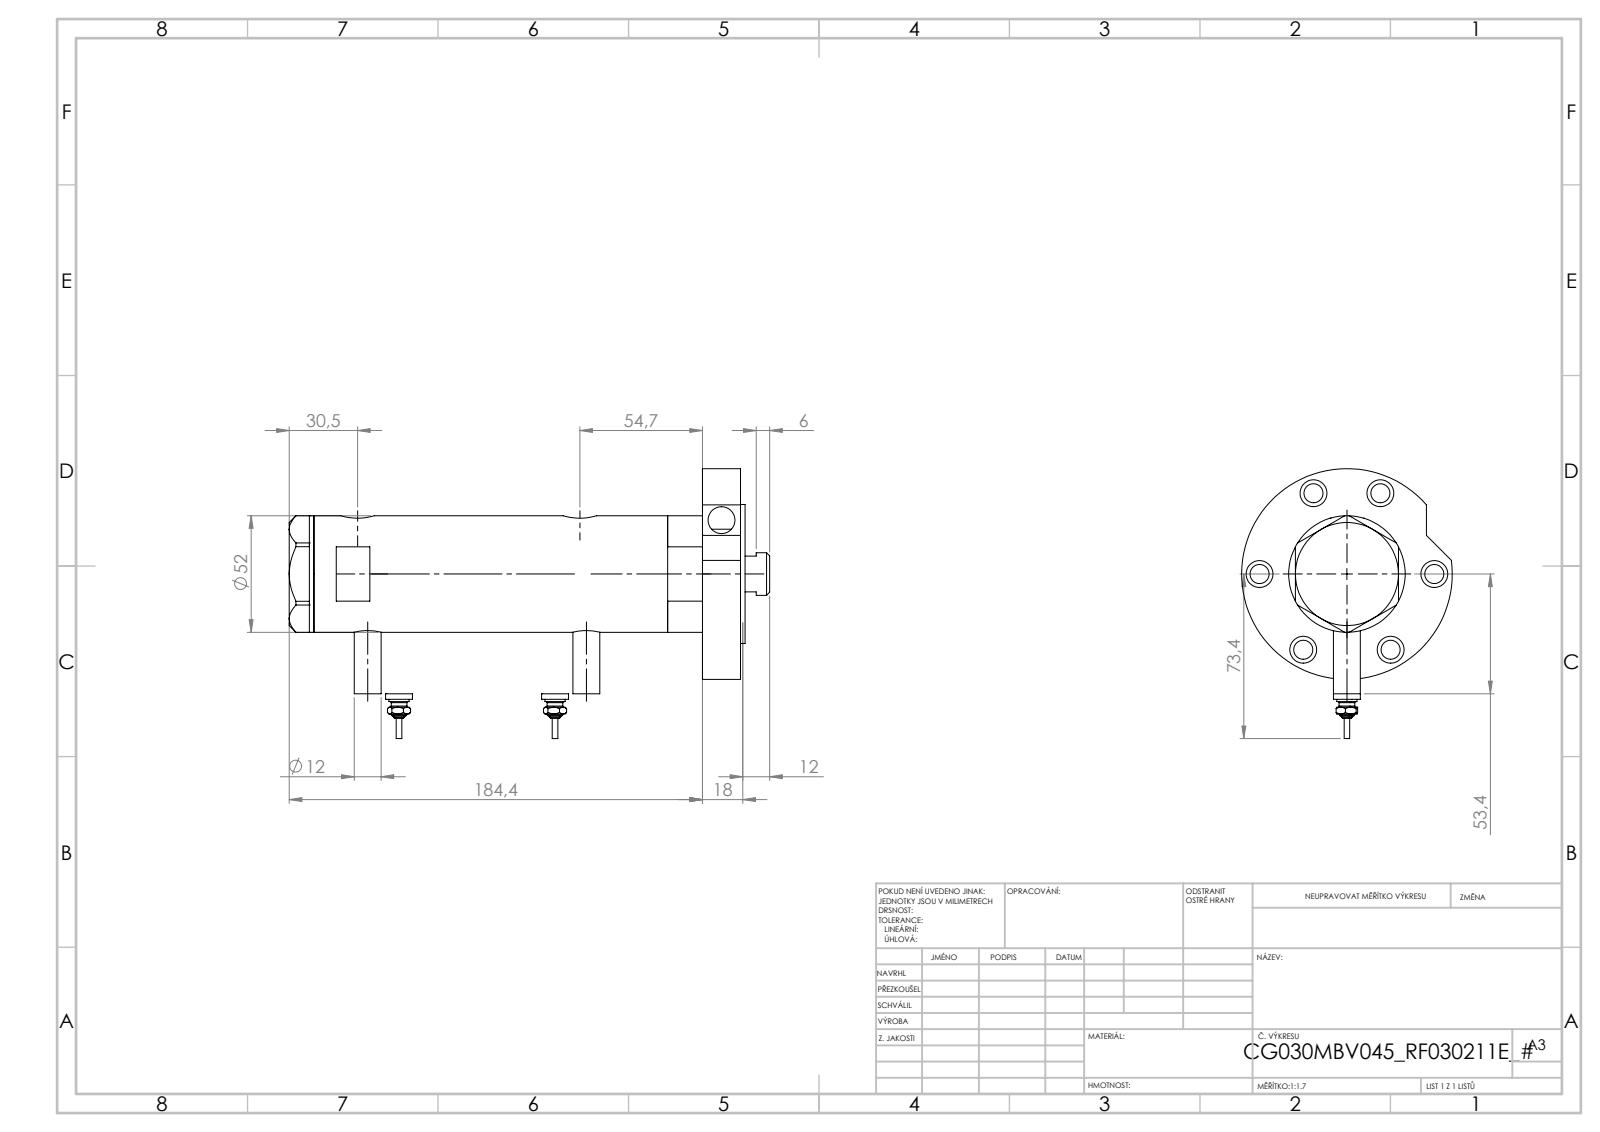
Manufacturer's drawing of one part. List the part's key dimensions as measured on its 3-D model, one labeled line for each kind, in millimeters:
Part name (STEP PRODUCT): V270CG_SWITCH; V270CG_MIDDLE; V270CG_RF211E; V270CG_BACK (+2 more)
STEP written by: SolidWorks 2019 (CONFIG_CONTROL_DESIGN)
Units: millimetres
Bodies: 7 solids, 290 faces (106 planar, 110 cylindrical, 74 other)
Overall size (bounding box): 194.02 × 105.3 × 94
Volume: 430 082 mm³ · Surface area: 105 238 mm²
Round holes (diameter × count): ⌀12 ×7, ⌀8.5 ×6, ⌀5 ×2, ⌀9.73 ×2, ⌀12.5 ×2, ⌀15 ×2, ⌀6.5 ×1, ⌀20 ×1, ⌀21.5 ×1, ⌀30 ×1, ⌀33 ×1, ⌀40 ×1
Round bosses / shafts (diameter × count): ⌀12 ×3, ⌀9 ×2, ⌀7 ×2, ⌀4.34 ×2, ⌀2.4 ×2, ⌀94 ×1, ⌀62 ×1, ⌀52 ×1
Main face-to-face distances: 17, 150.44, 167.44, 51.9, 2, 169.44, 98.54, 68.9, 70.9, 19
Hole centre spacings: 39, 2.9, 4.5, 43.34, 64.85, 67.55, 69.95, 71.75
